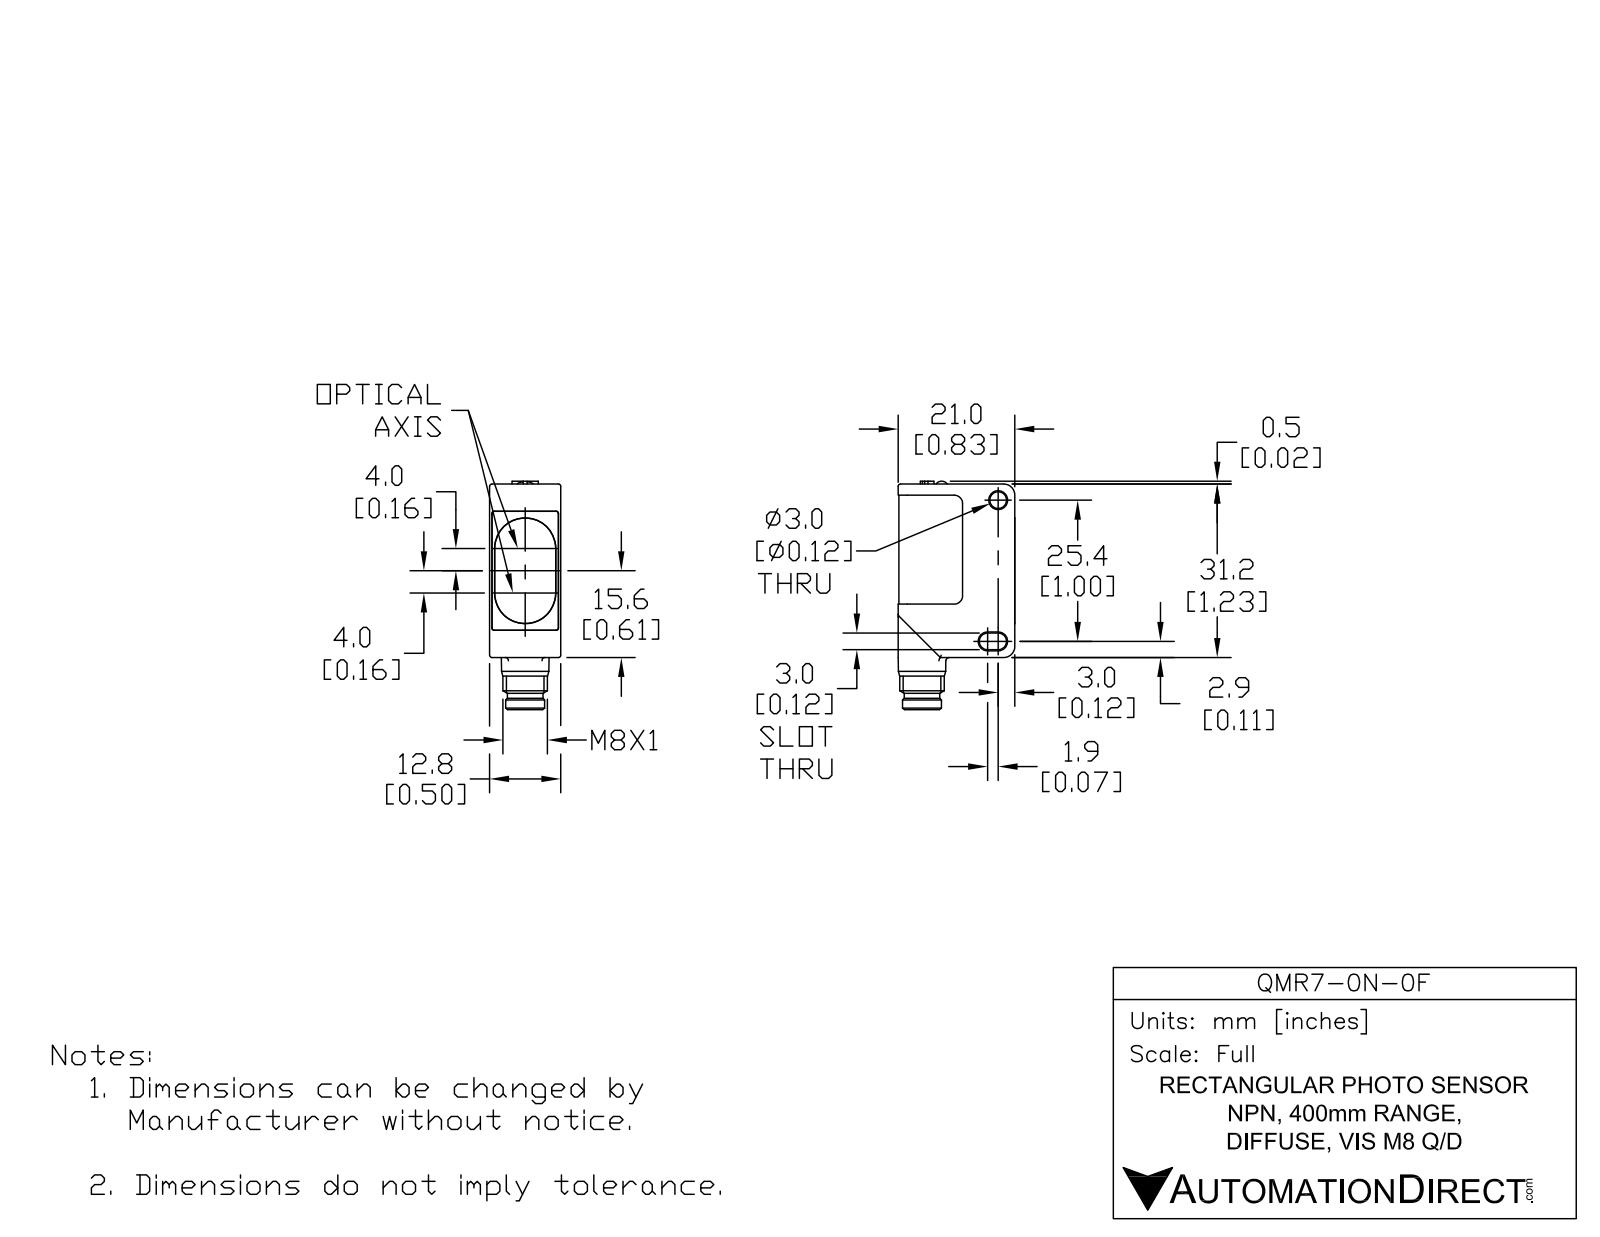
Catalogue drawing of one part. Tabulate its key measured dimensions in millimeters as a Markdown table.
| quantity | value |
| --- | --- |
| part name | QMR7-0N-0F |
| STEP written by | SolidWorks 2017 (AUTOMOTIVE_DESIGN) |
| units | millimeters |
| bodies | 7 solids, 272 faces (125 planar, 100 cylindrical, 47 other) |
| overall size | 41.1 × 21 × 12.8 |
| volume | 7 770 mm³ |
| surface area | 4 999 mm² |
| round holes (diameter × count) | 3 × 3, 5.8 × 1 |
| round bosses / shafts (diameter × count) | 1 × 4, 3.5 × 2, 8 × 1, 7 × 1, 6.4 × 1 |
| partial cylindrical surfaces (radius × count) | 0.4 × 10, 0.5 × 9, 1.5 × 6, 0.6 × 4, 1 × 4, 0.2 × 2, 1.1 × 2, 1.7 × 2 |
| main face-to-face distances | 12.6, 0.5, 12.8, 2.8, 0.4, 12.5, 12.4, 12.2, 1.5, 18.1 |
| hole center spacings | 1, 5.2, 6.2 |
